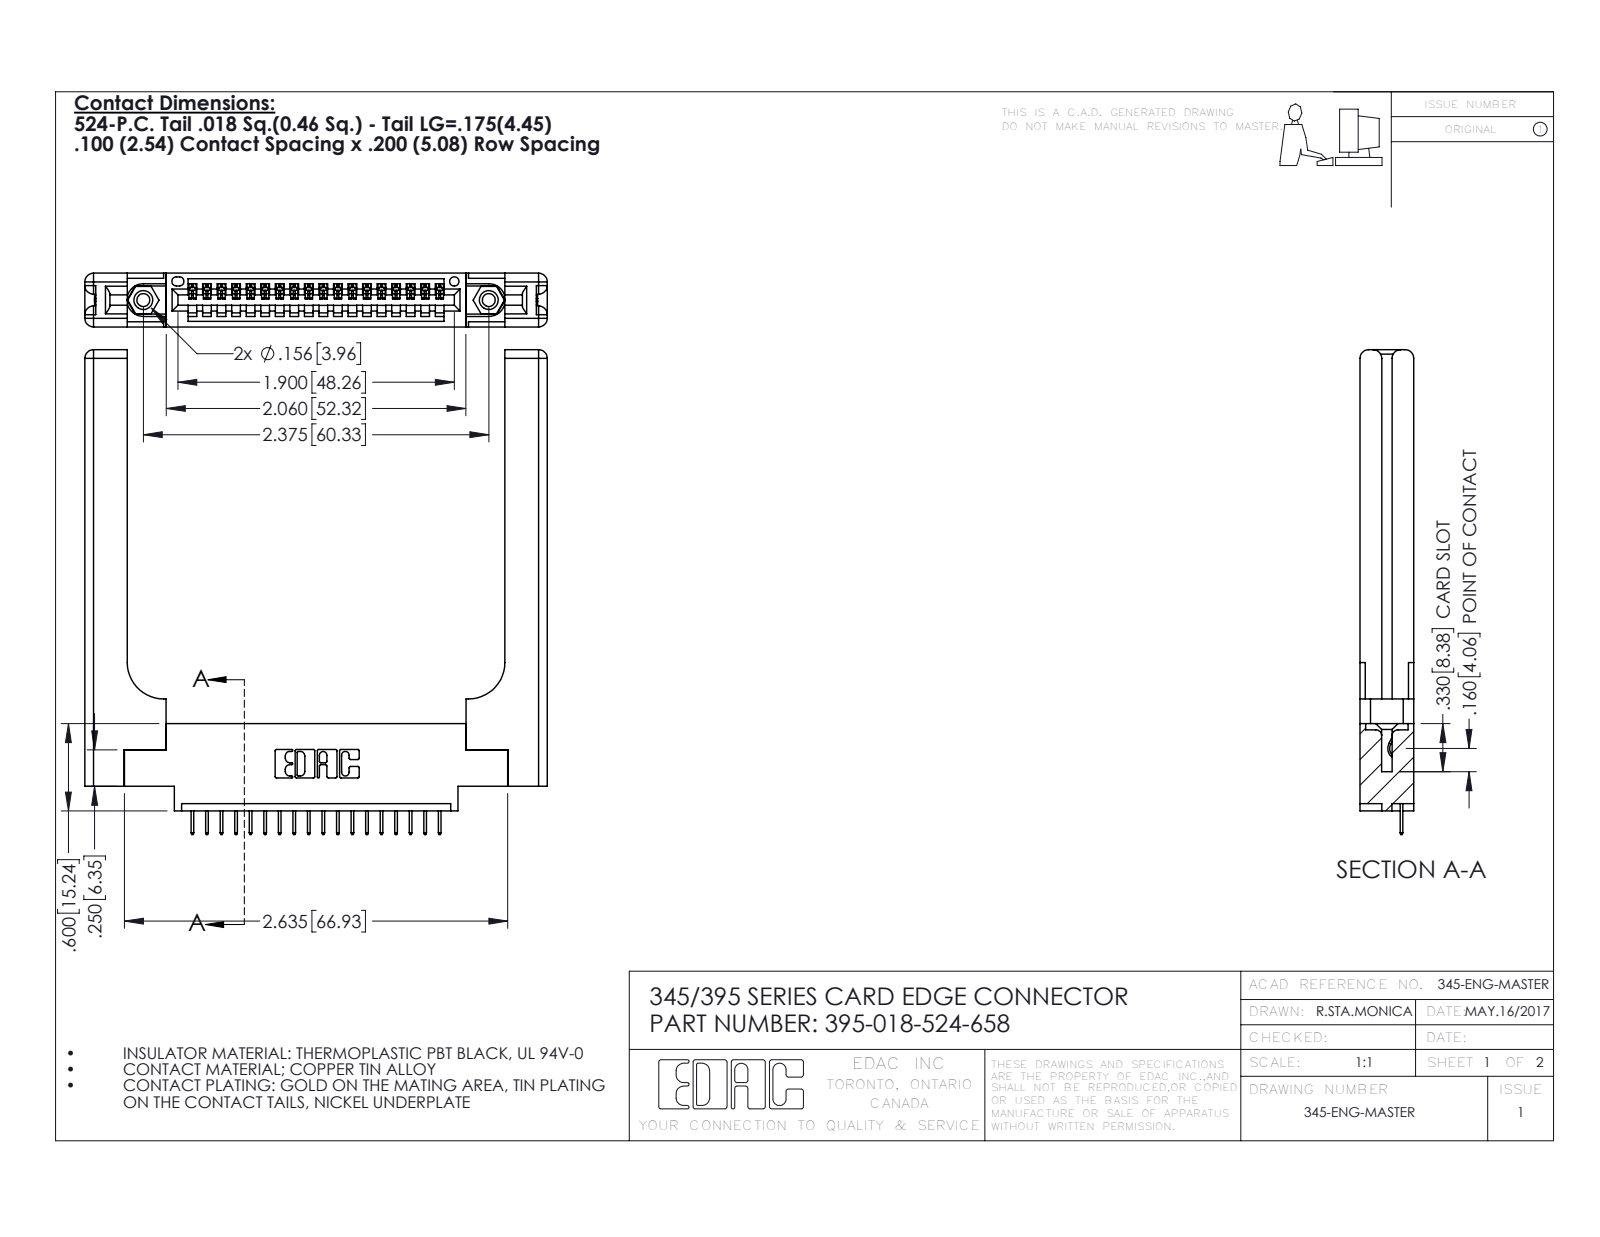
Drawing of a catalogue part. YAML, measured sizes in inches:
part_name: "345 Part_0.170 Offset - 0.156 Dia-TH; 345-292-001_345-293-124; 345-250-001_345-250-001-102; 395-018-524-658 (+1 more)"
step_written_by: "SolidWorks 2016 (CONFIG_CONTROL_DESIGN)"
units: inches
bodies: {solids: 23, faces: 1502, planar: 1060, cylindrical: 382, other: 60}
overall_size: [3.332, 3.179, 0.37]
volume: 0.964
surface_area: 22.57
round_holes:
  - {diameter: 0.089, count: 2}
  - {diameter: 0.125, count: 2}
  - {diameter: 0.156, count: 2}
  - {diameter: 0.064, count: 1}
round_bosses_or_shafts:
  - {diameter: 0.155, count: 2}
partial_cylinders:
  - {radius: 0.006, count: 36}
  - {radius: 0.01, count: 22}
  - {radius: 0.06, count: 16}
  - {radius: 0.007, count: 6}
  - {radius: 0.031, count: 6}
  - {radius: 0.026, count: 3}
  - {radius: 0.03, count: 2}
  - {radius: 0.031, count: 2}
face_to_face_distances: [0.37, 0.072, 0.298, 0.148, 0.15, 0.077, 0.22, 0.123, 0.12, 0.098]
hole_center_spacings: [0.27, 2.141, 2.375]
